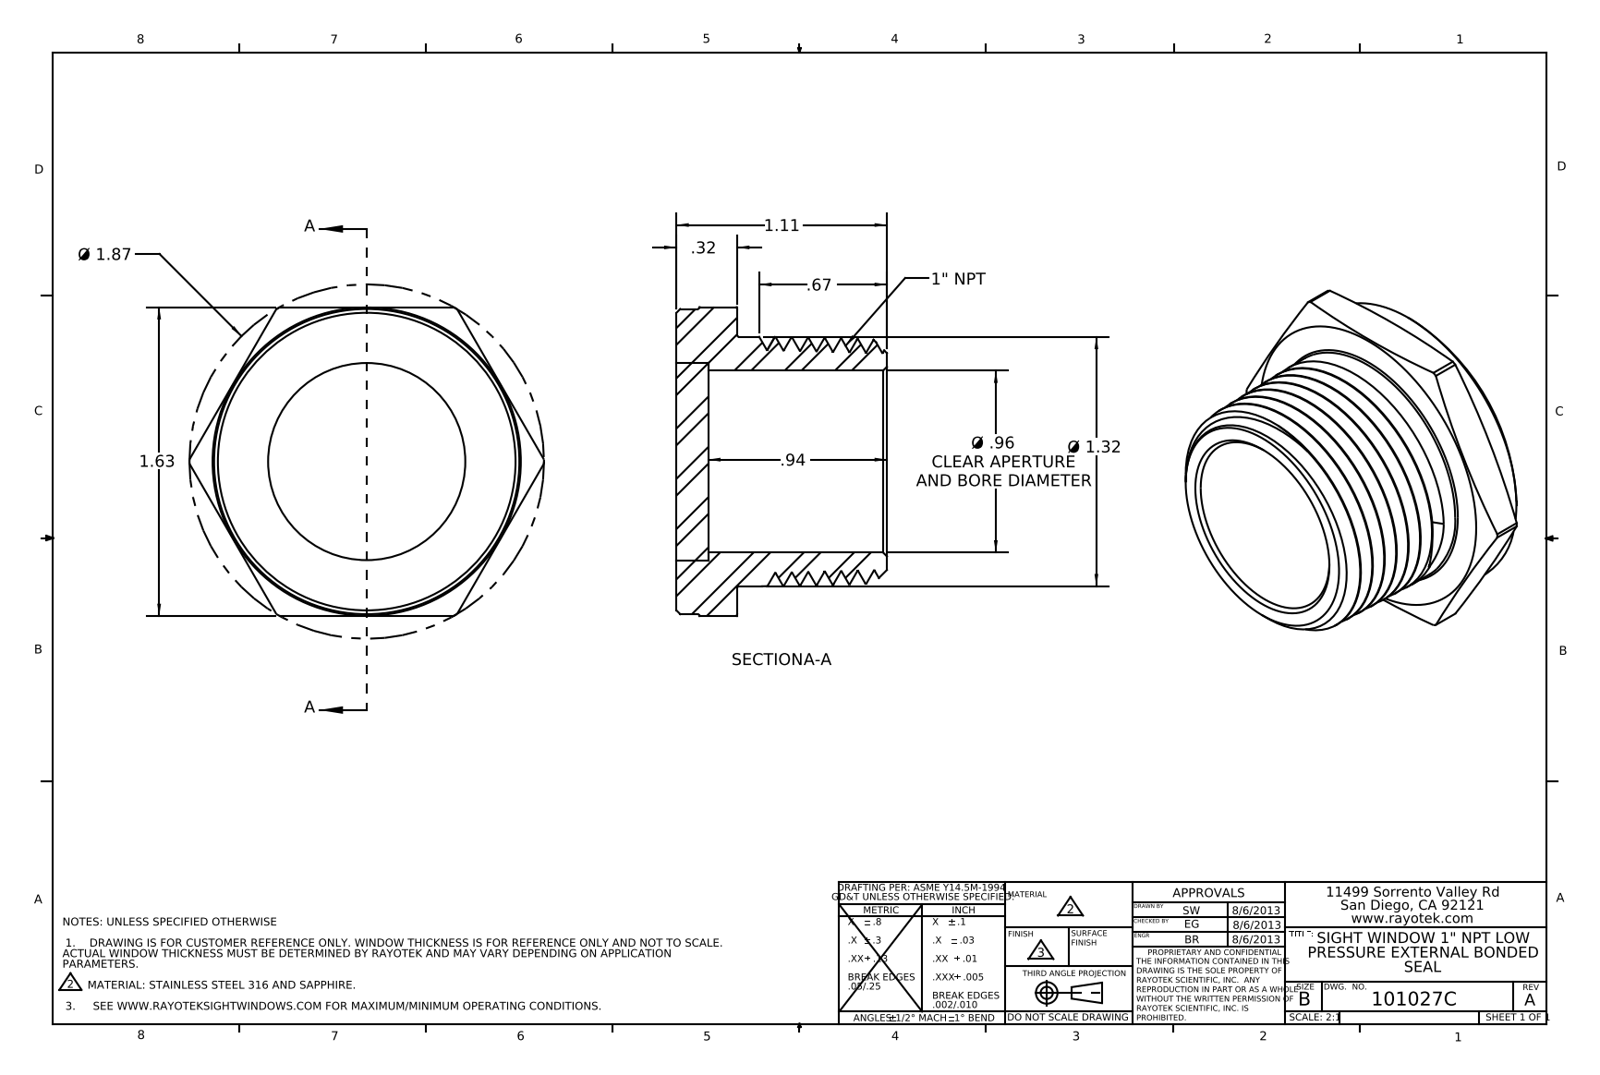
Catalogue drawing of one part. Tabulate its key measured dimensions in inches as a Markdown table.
| quantity | value |
| --- | --- |
| part name | 403027 |
| STEP written by | SolidWorks 2012 (AUTOMOTIVE_DESIGN) |
| units | inches |
| bodies | 2 solids, 65 faces (15 planar, 17 cylindrical, 33 other) |
| overall size | 1.87 × 1.63 × 1.11 |
| volume | 0.978 in³ |
| surface area | 15.27 in² |
| round holes (diameter × count) | 0.96 × 1, 1.04 × 1 |
| round bosses / shafts (diameter × count) | 1.61 × 1, 1.316 × 1 |
| partial cylindrical surfaces (radius × count) | 0.935 × 1 |
| main face-to-face distances | 0.168, 0.32, 0.152, 1.63, 1.11, 0.943, 0.79 |
